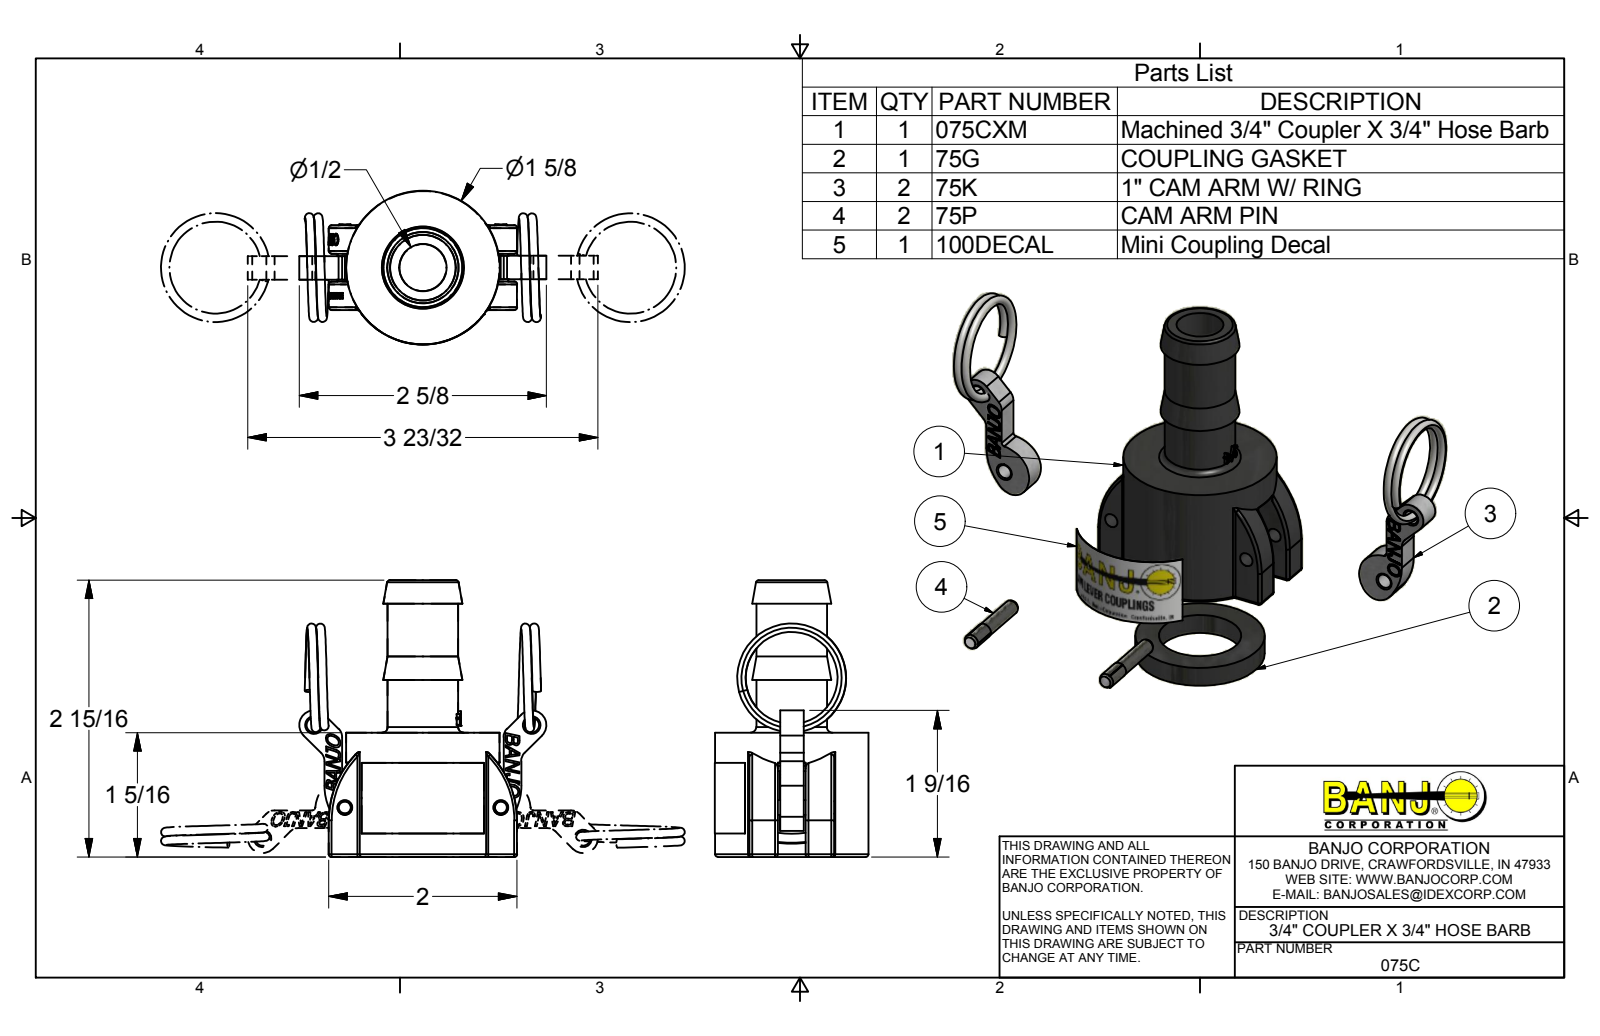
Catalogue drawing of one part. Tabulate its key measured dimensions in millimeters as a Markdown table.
| quantity | value |
| --- | --- |
| part name | 075CX; 075CXM; 75GFD; 75XK (+5 more) |
| STEP written by | Autodesk Inventor 2014 (AUTOMOTIVE_DESIGN) |
| units | millimeters |
| bodies | 9 solids, 804 faces (419 planar, 91 cylindrical, 294 other) |
| overall size | 74.68 × 66.69 × 41.47 |
| volume | 36 653 mm³ |
| surface area | 24 851 mm² |
| round holes (diameter × count) | 3.96 × 4, 4.04 × 2, 12.7 × 1, 22.22 × 1, 32.61 × 1, 36.12 × 1 |
| round bosses / shafts (diameter × count) | 4.17 × 2, 41.4 × 1, 34.92 × 1, 19.05 × 1 |
| partial cylindrical surfaces (radius × count) | 0.76 × 18, 3.17 × 4, 0.79 × 2, 3.97 × 2, 15.08 × 2, 10.29 × 1, 20.76 × 1, 24.89 × 1 |
| main face-to-face distances | 4.85, 6.35, 5.54, 10.39, 7.68, 15.18, 0.51, 0.64, 6.86, 8.19 |
| hole center spacings | 23.73, 55.1, 42.08, 58.76 |
